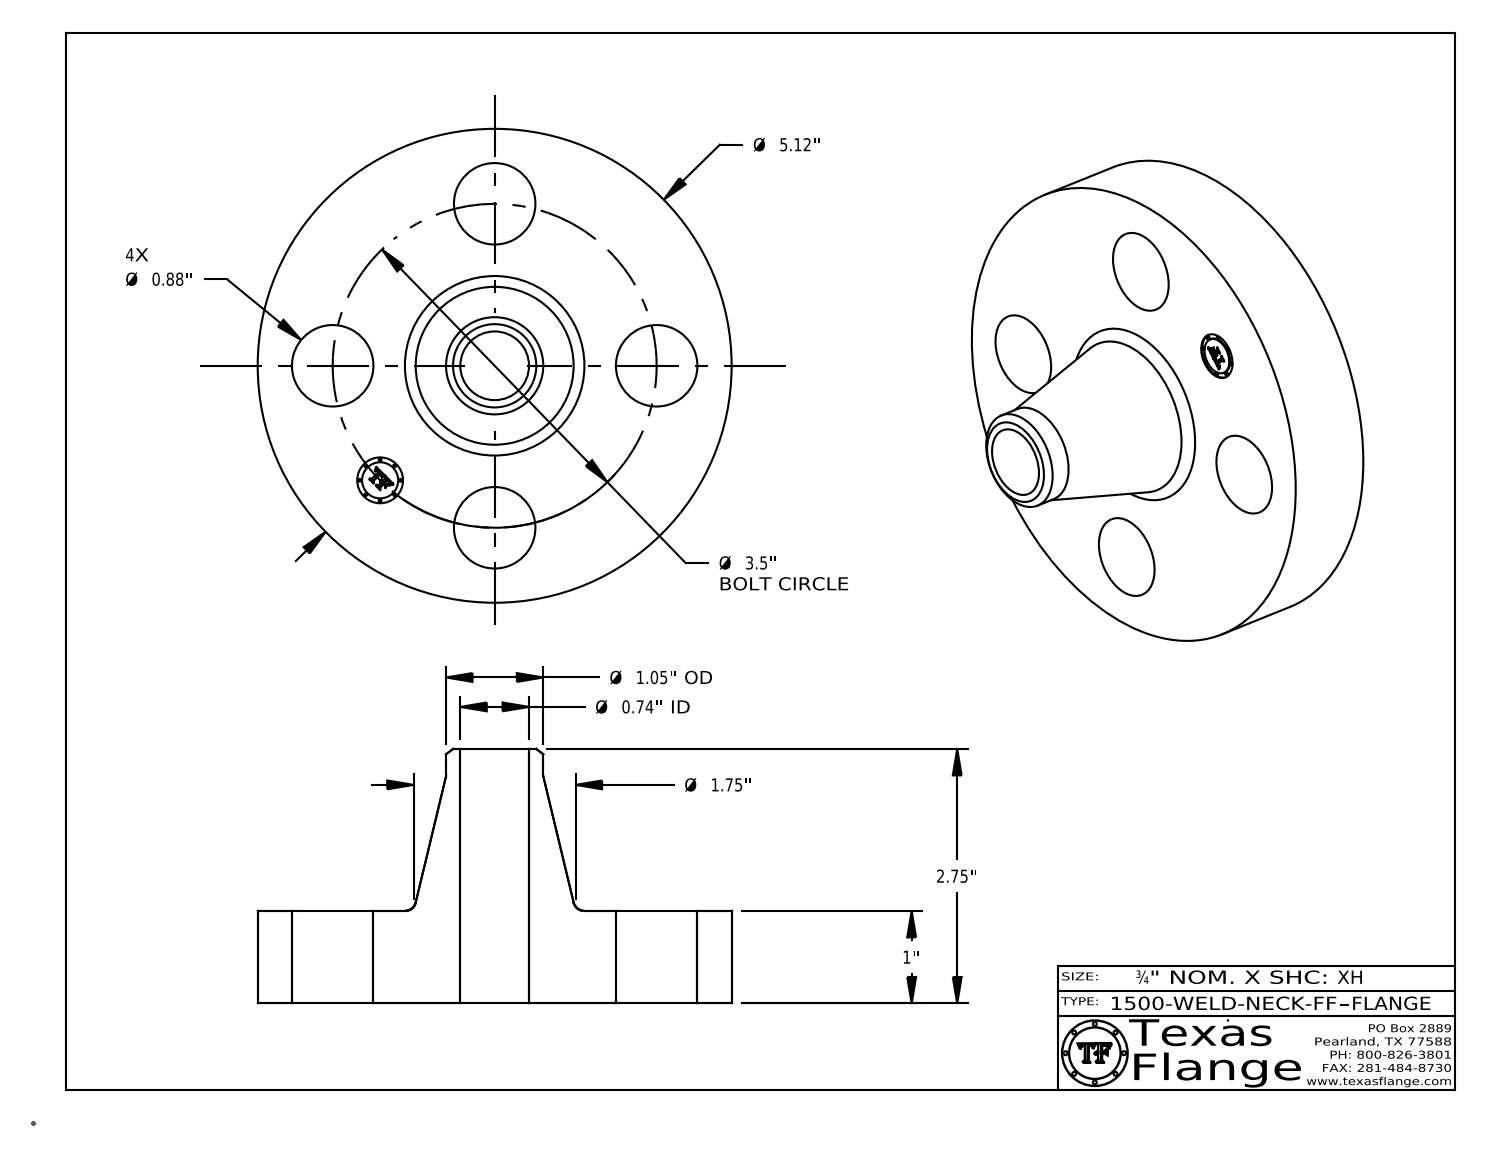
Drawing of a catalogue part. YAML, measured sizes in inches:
part_name: "1500-WELD-NECK-FF"
step_written_by: "CATIA V5 STEP AP214 (AUTOMOTIVE_DESIGN)"
units: inches
bodies: {solids: 1, faces: 408, planar: 368, cylindrical: 34, other: 6}
overall_size: [5.12, 5.12, 2.75]
volume: 19.51
surface_area: 74.83
round_holes:
  - {diameter: 0.88, count: 4}
  - {diameter: 0.495, count: 1}
  - {diameter: 0.742, count: 1}
round_bosses_or_shafts:
  - {diameter: 0.03, count: 8}
  - {diameter: 5.12, count: 1}
  - {diameter: 1.05, count: 1}
  - {diameter: 0.39, count: 1}
face_to_face_distances: [1, 2.75, 1.75, 0.015, 0.985, 1.765, 0.148, 0.145, 0.027, 0.096]
hole_center_spacings: [1.75, 2.475, 1.339, 3.233, 3.5]
